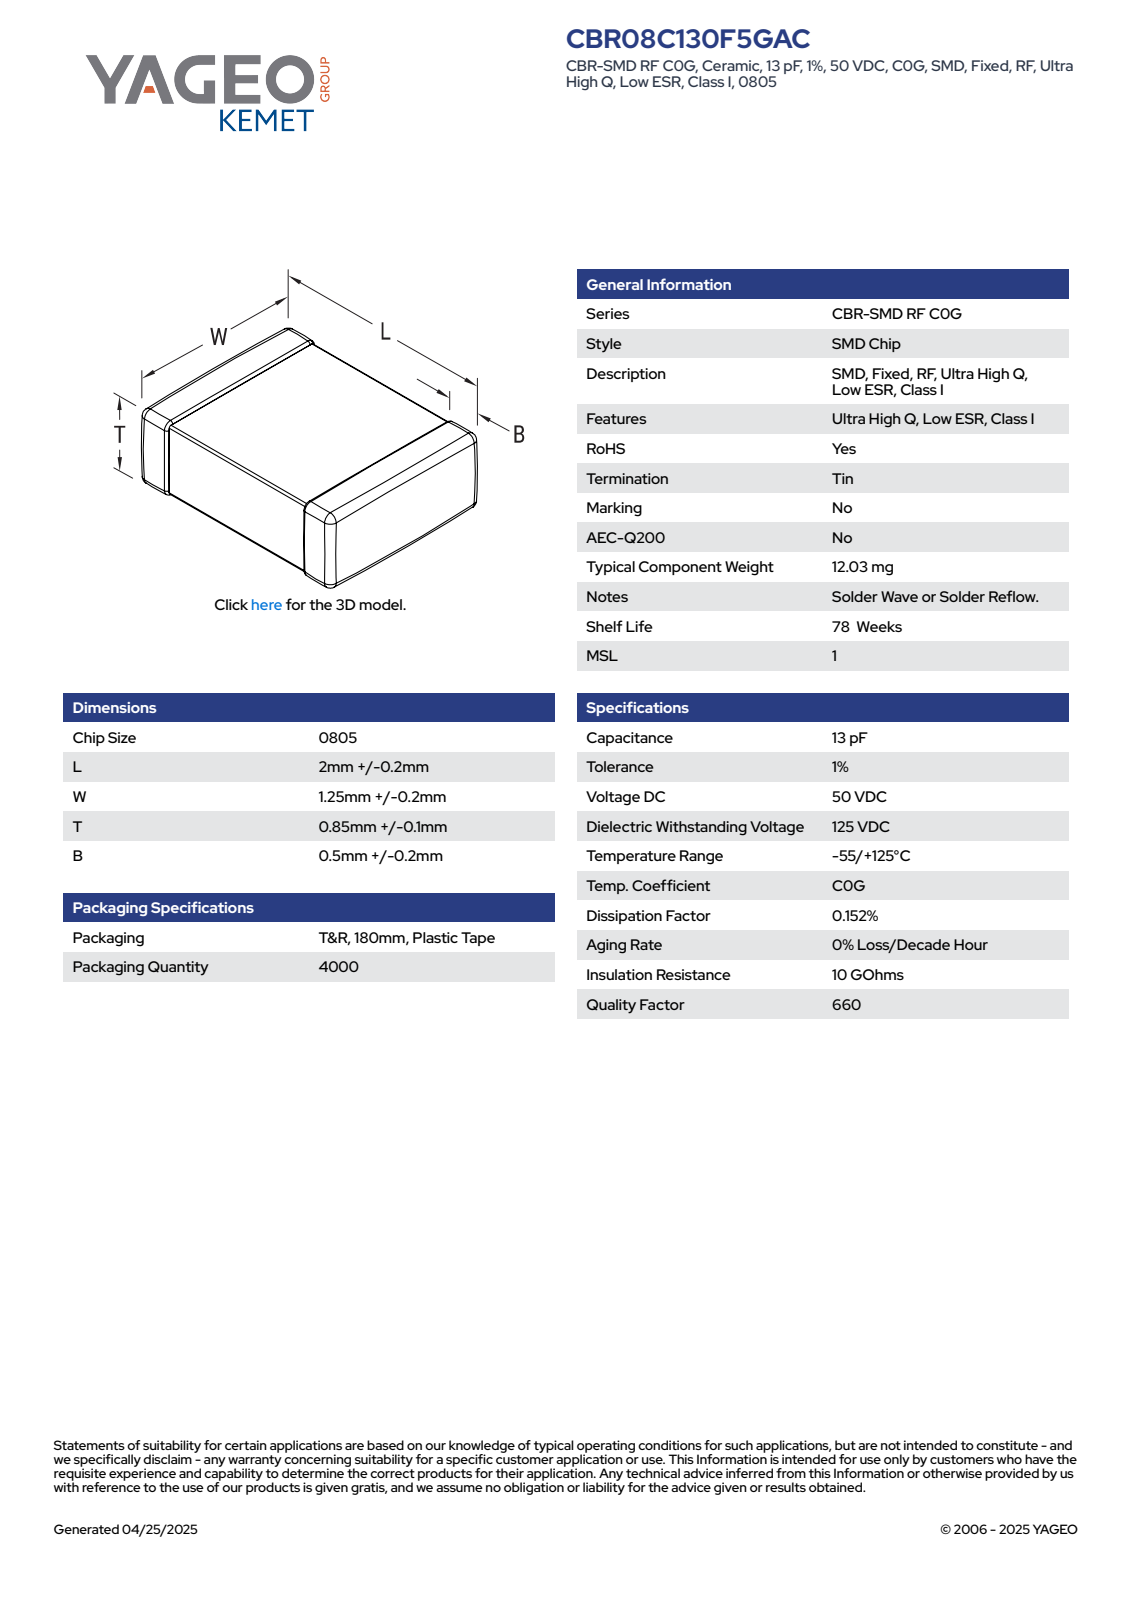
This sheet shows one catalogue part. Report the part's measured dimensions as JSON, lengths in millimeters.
{"part_name": "CCS_CCSTDNOS_0805_L2.2W1.45T0.95B0.7", "step_written_by": "SolidWorks 2014 (AUTOMOTIVE_DESIGN)", "units": "millimeters", "bodies": {"solids": 4, "faces": 121, "planar": 71, "cylindrical": 34, "other": 16}, "overall_size": [2.2, 1.45, 0.95], "volume_mm3": 3, "surface_area_mm2": 13, "face_to_face_distances": [0.92, 0.95, 1.42, 2.2, 1.45, 0.89, 1.39, 0.68, 0.65, 0.77]}
